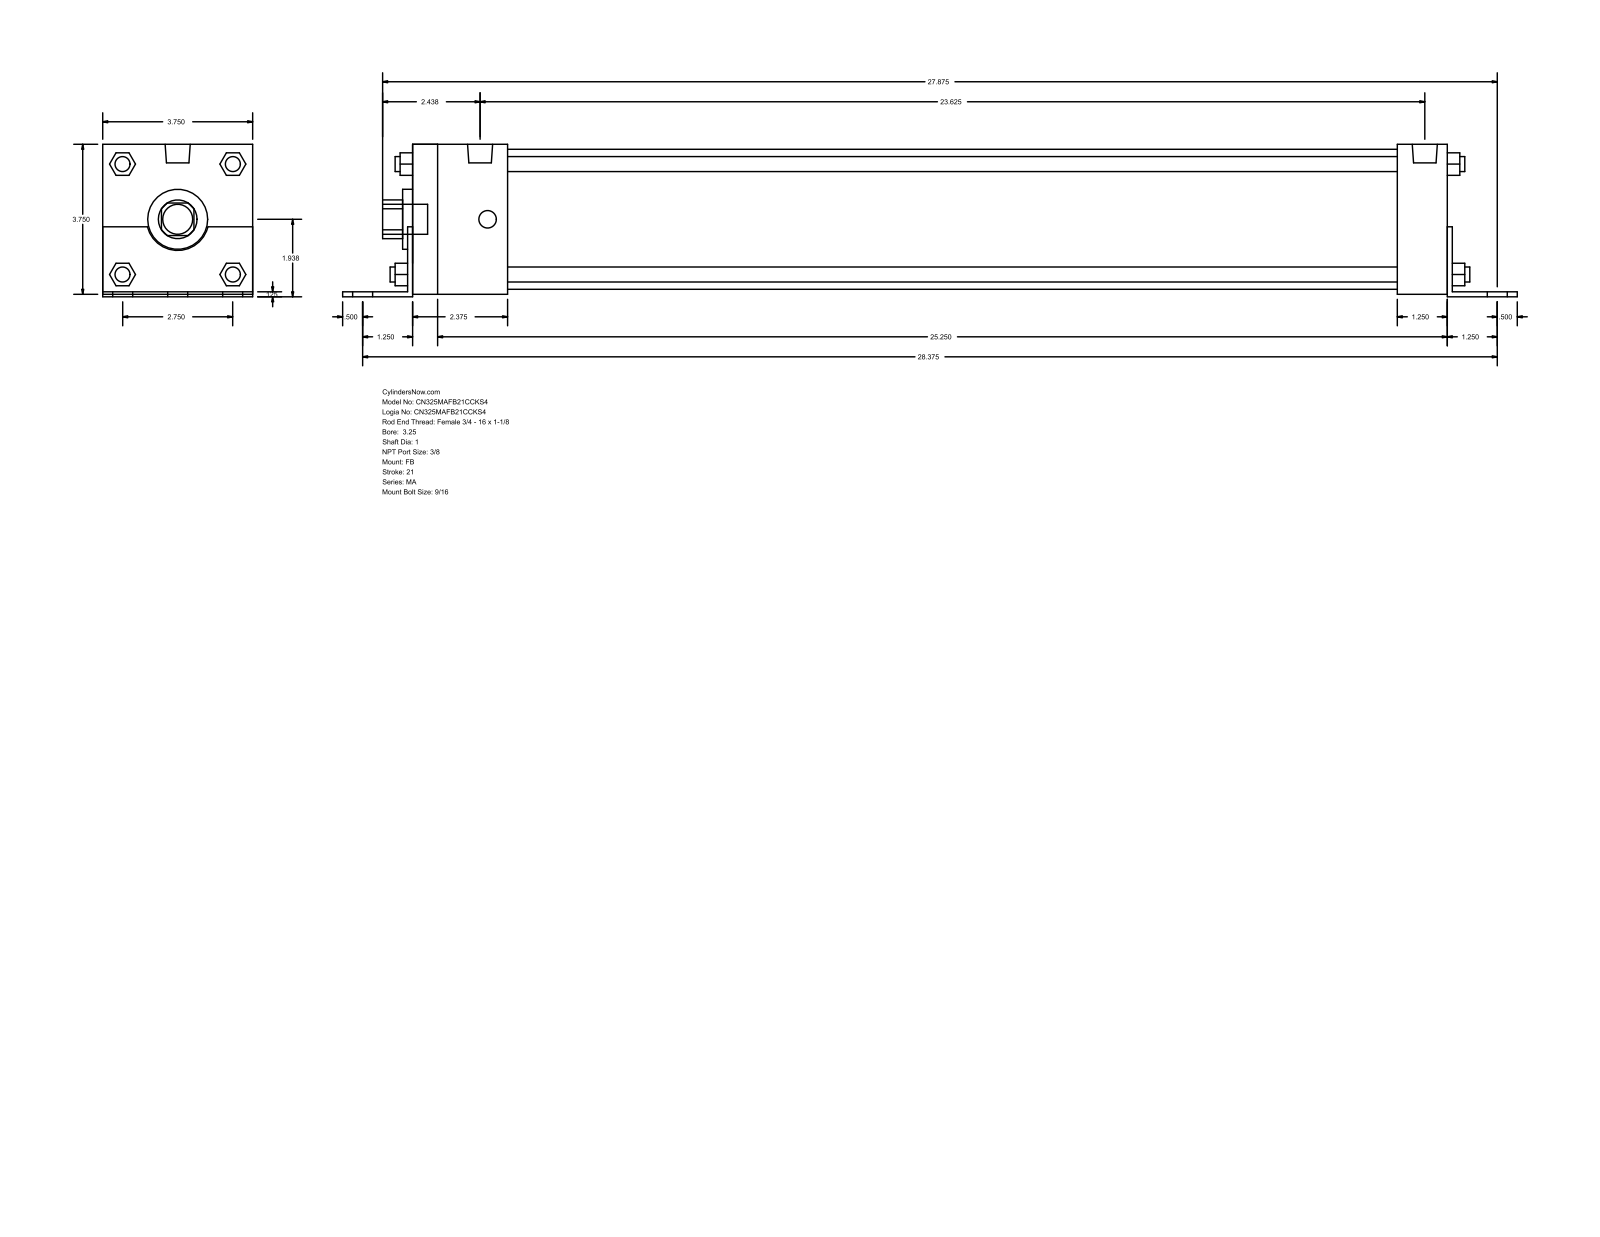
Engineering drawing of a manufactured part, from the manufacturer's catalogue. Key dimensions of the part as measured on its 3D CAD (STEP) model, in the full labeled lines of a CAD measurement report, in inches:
Part name (STEP PRODUCT): MA_FB__0325_1
STEP written by: GSSL Pune (CONFIG_CONTROL_DESIGN)
Units: inches
Bodies: 0 solids, 140 faces (105 planar, 35 cylindrical, 0 other)
Overall size (bounding box): 29.375 × 3.813 × 3.75
Round holes (diameter × count): ⌀1 ×1, ⌀1.5 ×1, ⌀3.5 ×1
Round bosses / shafts (diameter × count): ⌀0.563 ×6, ⌀0.437 ×4, ⌀0.375 ×4, ⌀0.627 ×2, ⌀0.75 ×1
Partial cylindrical surfaces — rounded edges, fillets, slot ends (radius × count): R0.484 ×1, R0.78 ×1
Main face-to-face distances: 3.75, 0.125, 0.063, 3.812, 0.062, 3.687, 0.125, 25.875, 26.125, 26
